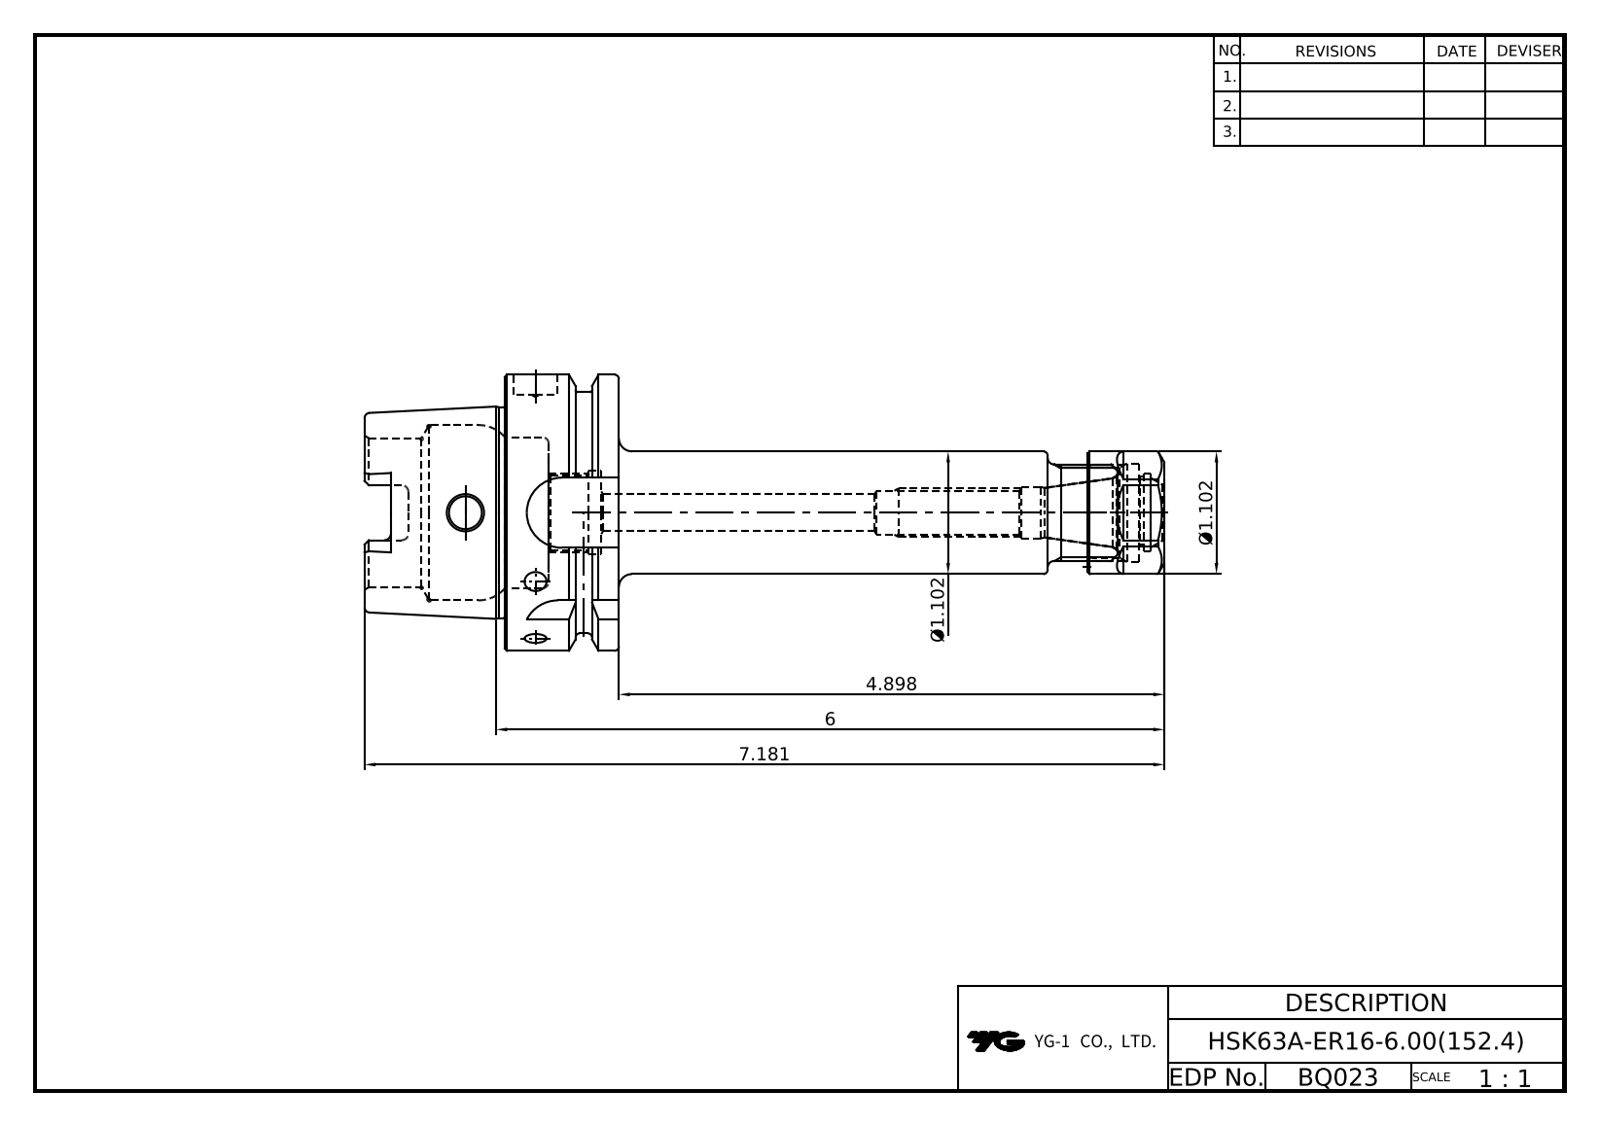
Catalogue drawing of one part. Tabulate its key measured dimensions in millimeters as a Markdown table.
| quantity | value |
| --- | --- |
| part name | HSK63A-ER16-152.4; LO-HSK63A-ER16-152.4; ER16NUT |
| STEP written by | Autodesk Inventor 2022 (AUTOMOTIVE_DESIGN) |
| units | millimeters |
| bodies | 2 solids, 153 faces (61 planar, 43 cylindrical, 49 other) |
| overall size | 184.4 × 63 × 63 |
| volume | 145 444 mm³ |
| surface area | 39 368 mm² |
| round holes (diameter × count) | 1 × 1, 7.5 × 1, 8 × 1, 9.4 × 1, 10 × 1, 11.8 × 1, 12.8 × 1, 16.92 × 1, 17.7 × 1, 19 × 1, 20.6 × 1, 22.5 × 1 |
| round bosses / shafts (diameter × count) | 63 × 1, 55 × 1, 48.04 × 1, 28 × 1, 22 × 1 |
| partial cylindrical surfaces (radius × count) | 1.5 × 6, 2.88 × 4, 8 × 4, 7.7 × 2 |
| main face-to-face distances | 26, 16, 10, 32, 42, 58, 22, 25, 53, 4 |
| hole center spacings | 12 |
